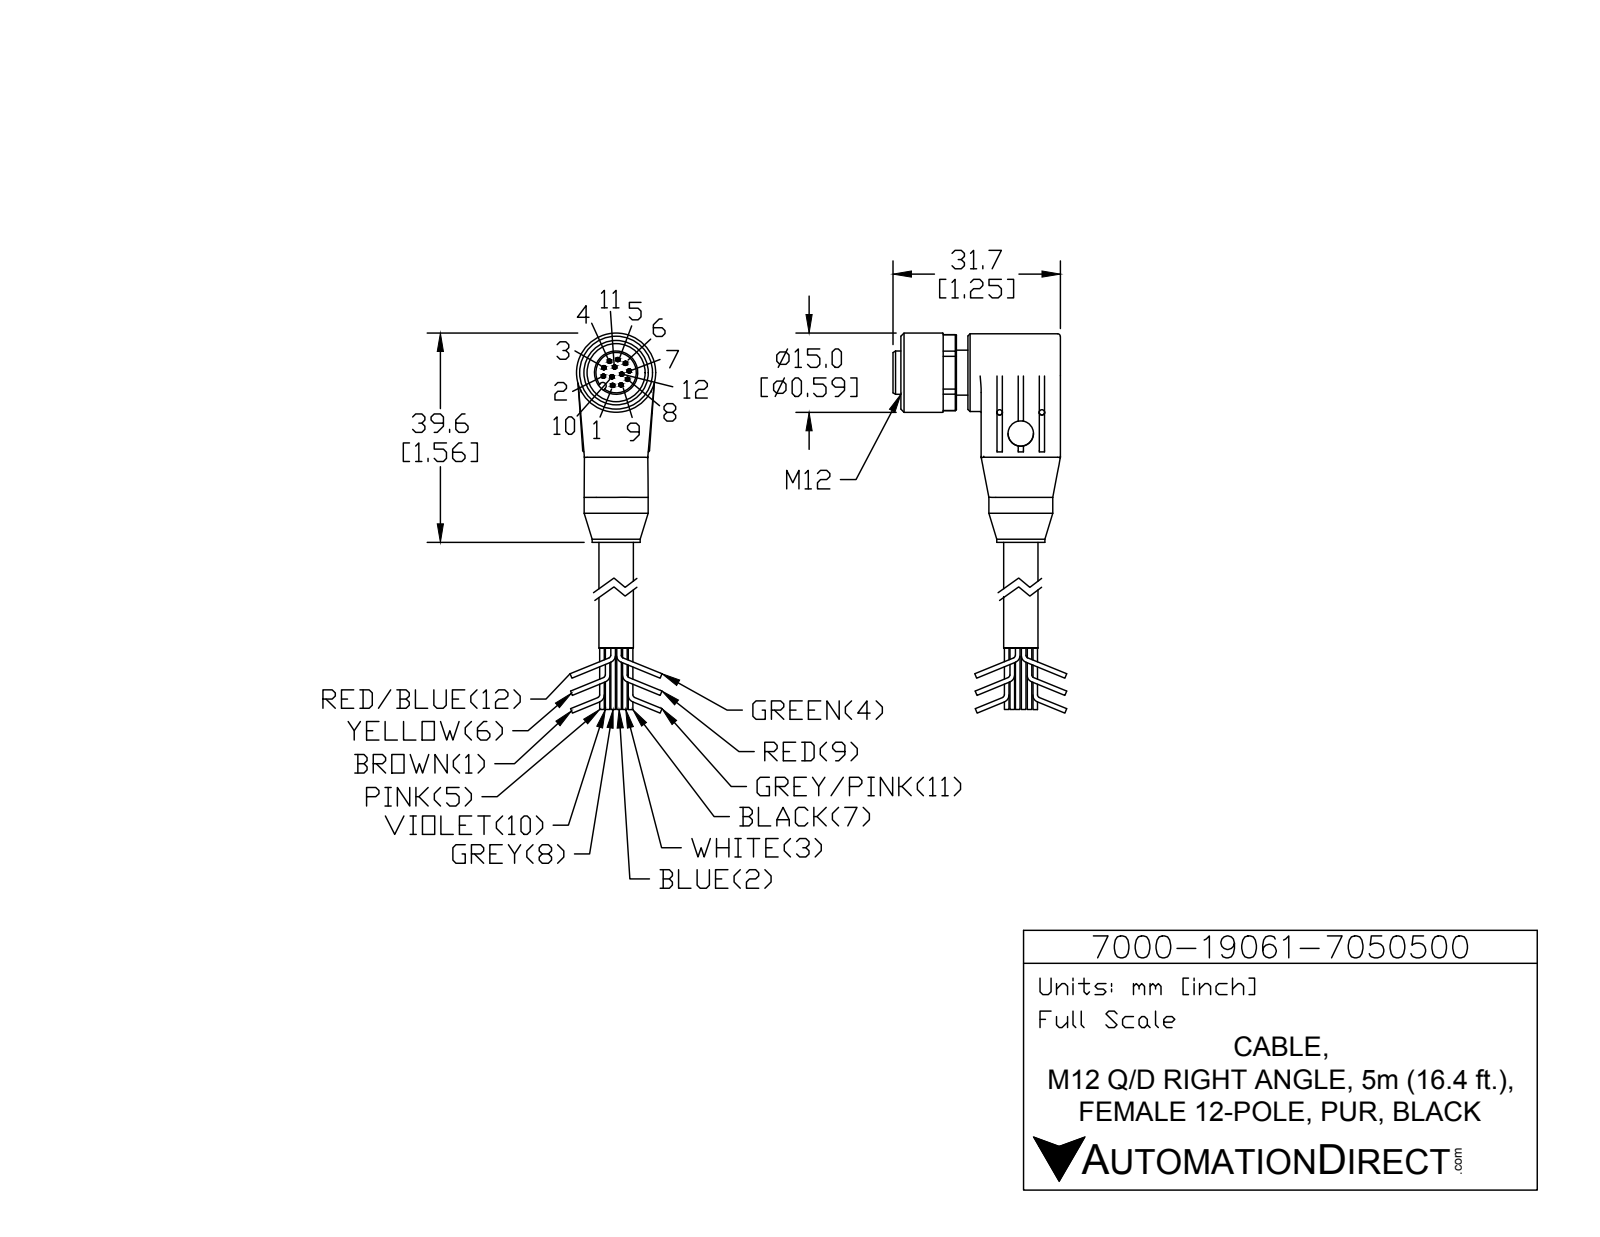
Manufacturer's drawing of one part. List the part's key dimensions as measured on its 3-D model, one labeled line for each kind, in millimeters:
Part name (STEP PRODUCT): 7000-19061-7050500
STEP written by: SolidWorks 2015 (AUTOMOTIVE_DESIGN)
Units: millimetres
Bodies: 1 solid, 186 faces (77 planar, 75 cylindrical, 34 other)
Overall size (bounding box): 59.6 × 31.7 × 15
Volume: 9 096 mm³ · Surface area: 4 119 mm²
Round holes (diameter × count): ⌀0.8 ×12, ⌀1.05 ×4, ⌀4.8 ×1, ⌀11 ×1
Round bosses / shafts (diameter × count): ⌀15 ×1, ⌀14.7 ×1, ⌀12.1 ×1, ⌀9.1 ×1, ⌀8.5 ×1, ⌀8.2 ×1, ⌀6.5 ×1
Partial cylindrical surfaces — rounded edges, fillets, slot ends (radius × count): R0.5 ×4, R0.3 ×2, R0.65 ×1, R7.2 ×1
Main face-to-face distances: 2.5, 15, 4.7, 17.5, 19.7, 2.2, 3, 7.7, 12, 16.7
Hole centre spacings: 2.5, 1.61, 4.17, 3.05, 4.84, 4.99, 1.1, 4.61
